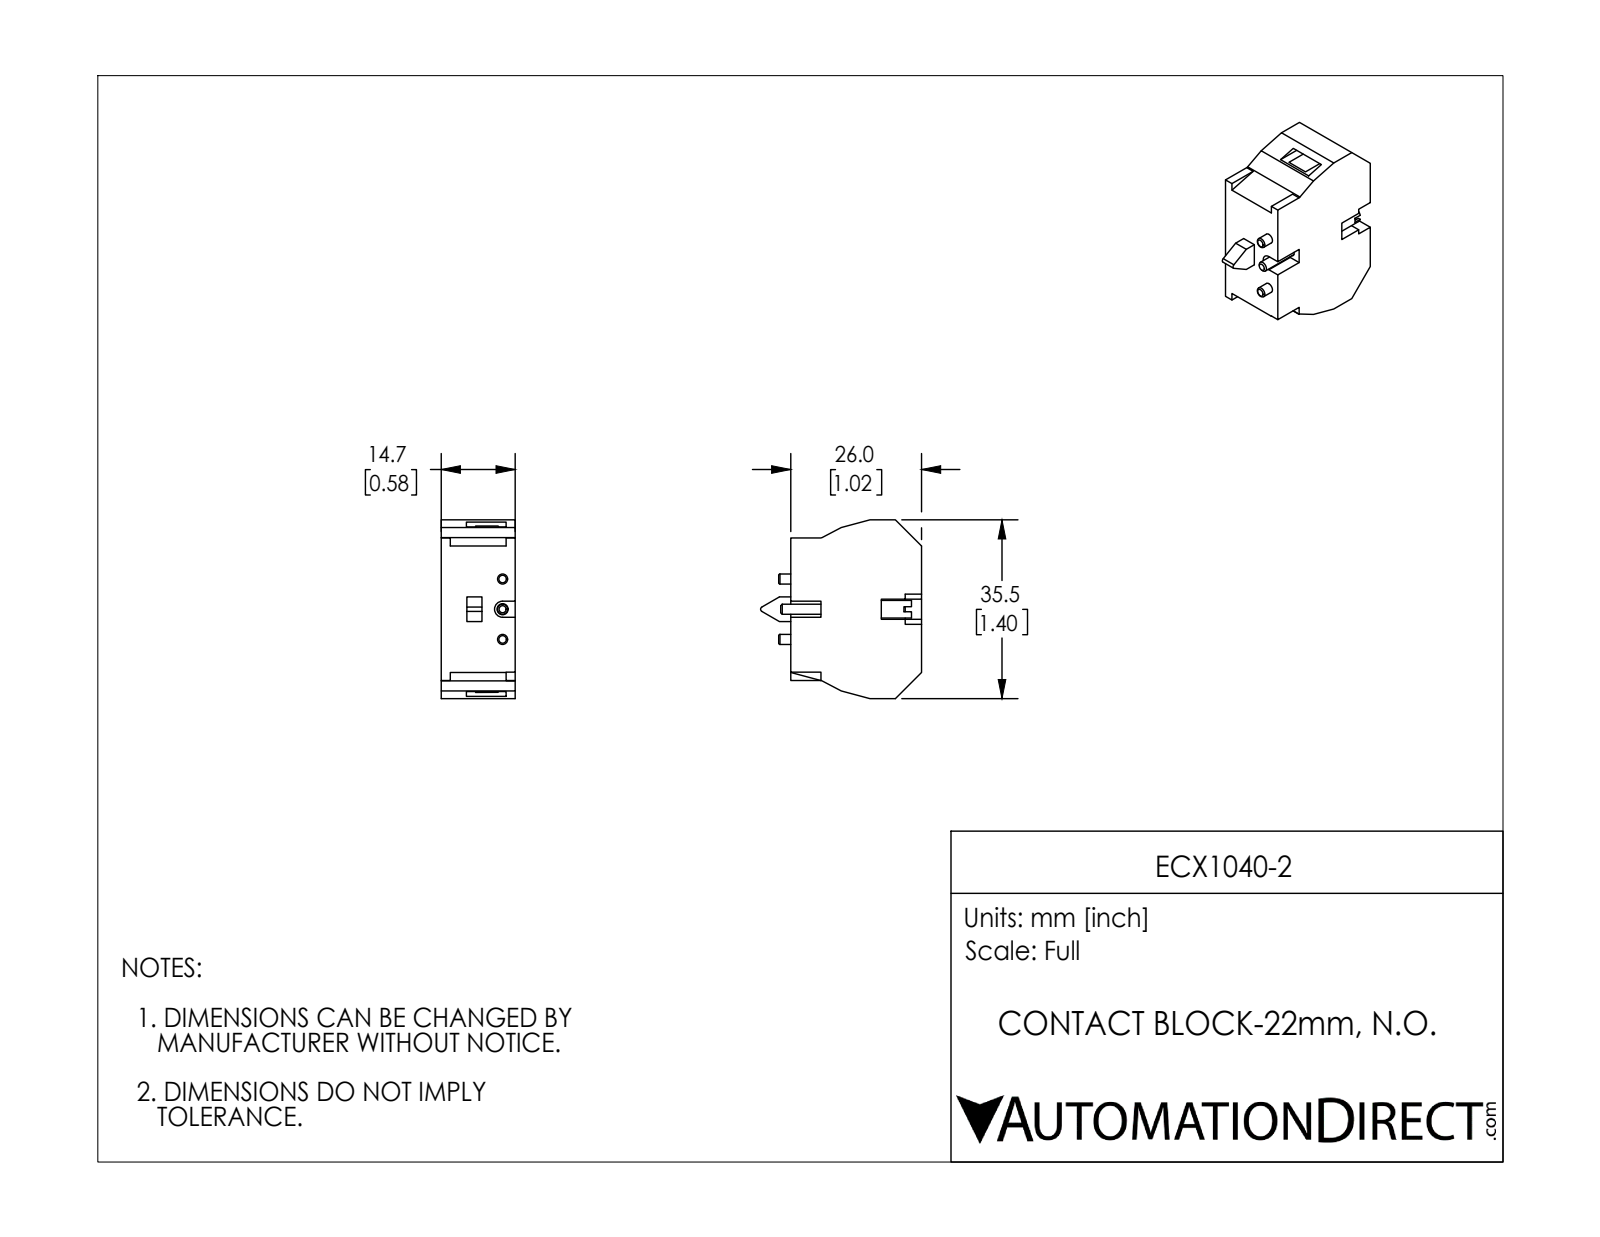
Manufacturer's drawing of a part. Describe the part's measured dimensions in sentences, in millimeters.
The part is named "ECX1040-2". Its 3-D file was written by "SolidWorks 2016 (AUTOMOTIVE_DESIGN)". It is 1 solid with 93 faces: 75 planar, 14 cylindrical and 4 other. Overall it measures 35.54 by 32 by 14.7 millimeters. Its volume is 10 661 cubic millimeters and its surface area 4 346 square millimeters. Round holes: 2 of diameter 2, 1 of diameter 2.2. Partial cylindrical surfaces (rounded edges, fillets, slot ends): 1 of radius 0.5, 1 of radius 1.6, 1 of radius 2. The main face-to-face distances are 14.7, 26, 6.84, 7.86, 0.45, 12.9, 6.87, 28.67, 0.95, 35.09. The hole center spacings are 6, 12.
